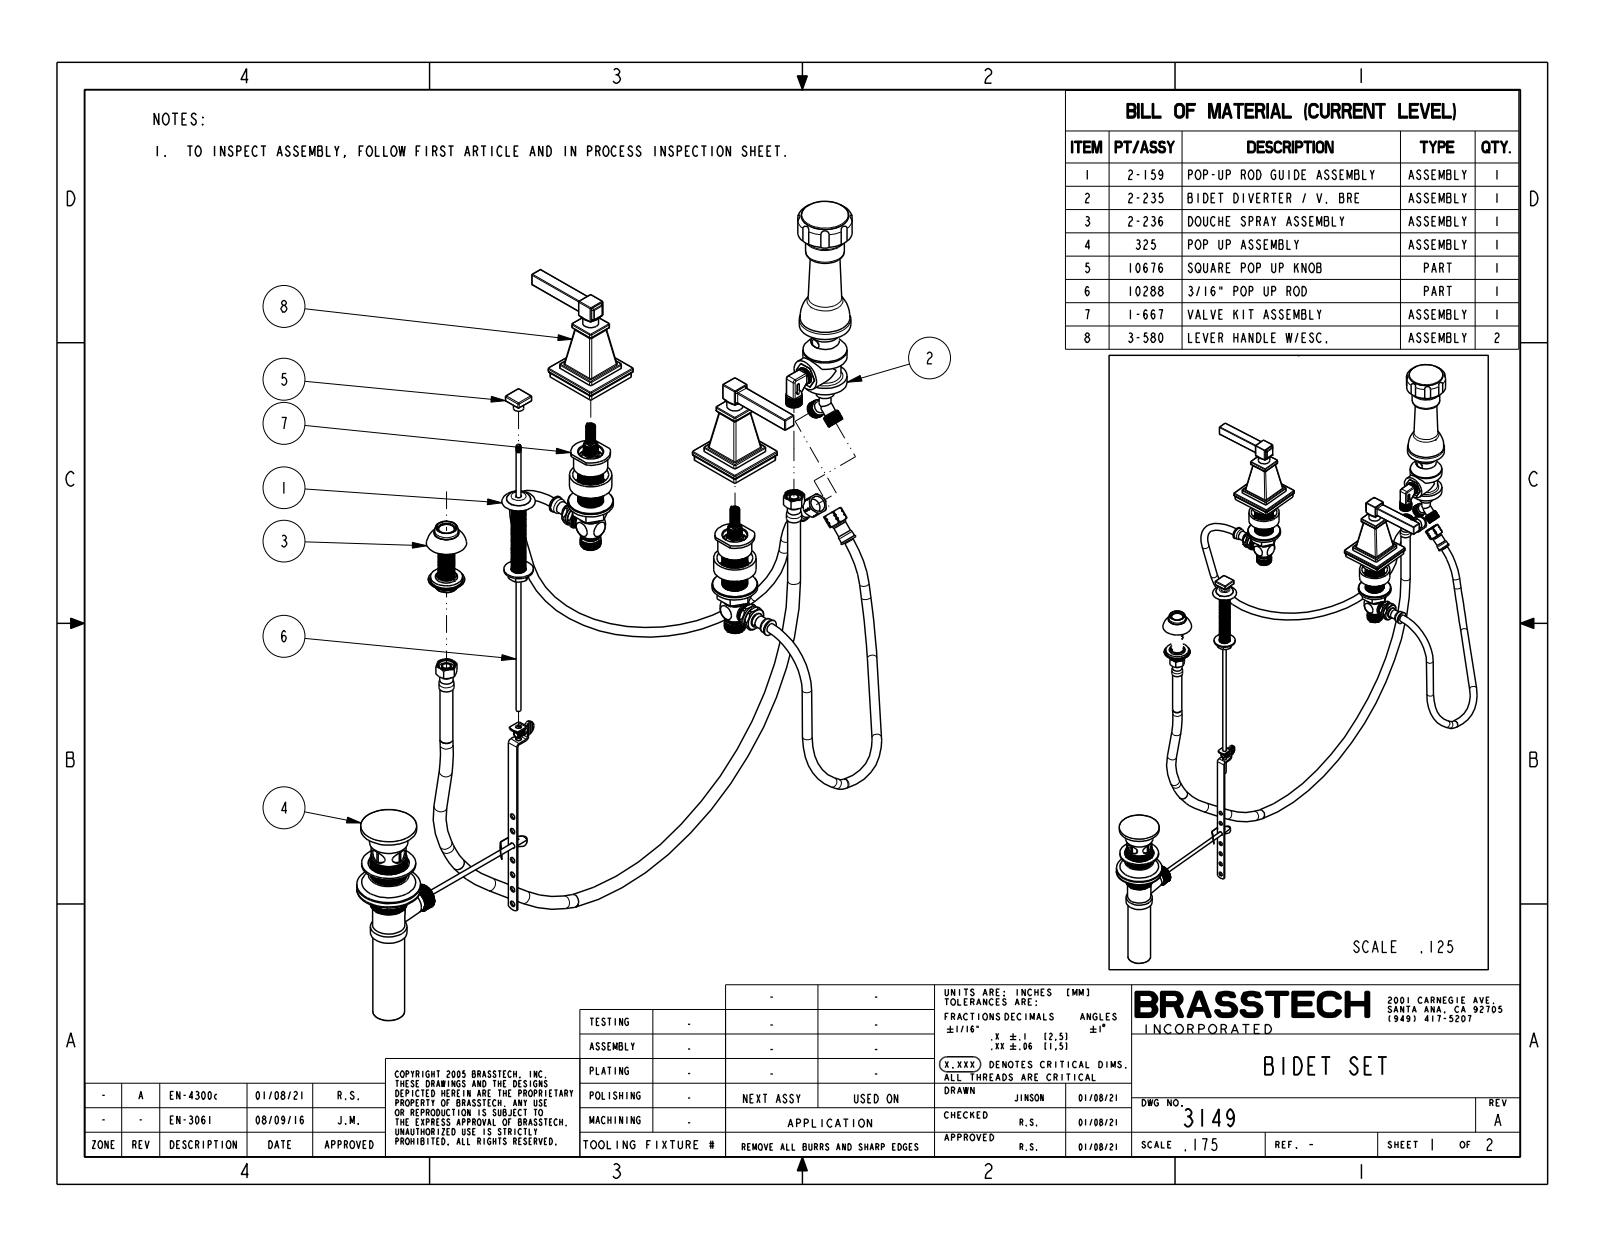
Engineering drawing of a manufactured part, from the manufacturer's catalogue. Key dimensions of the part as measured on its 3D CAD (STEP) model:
Part name (STEP PRODUCT): 3149
STEP written by: CREO PARAMETRIC BY PTC INC, 2018400 (CONFIG_CONTROL_DESIGN)
Units: inches
Bodies: 5 solids, 623 faces (133 planar, 244 cylindrical, 246 other)
Overall size (bounding box): 22.855 × 14.063 × 5.353
Volume: 25.54 in³ · Surface area: 116.5 in²
Round holes (diameter × count): ⌀0.625 ×1, ⌀0.792 ×1, ⌀0.94 ×1
Round bosses / shafts (diameter × count): ⌀0.625 ×2, ⌀0.506 ×2, ⌀2.025 ×1, ⌀1.52 ×1, ⌀0.925 ×1, ⌀0.775 ×1, ⌀0.4 ×1
Partial cylindrical surfaces — rounded edges, fillets, slot ends (radius × count): R0.03 ×76, R0.06 ×56, R0.04 ×12, R0.09 ×12, R0.21 ×8, R0.23 ×8, R0.357 ×1, R1.077 ×1
Main face-to-face distances: 0.41, 0.5, 7.88, 0.593, 0.093, 3.035, 3.535, 2.625, 3.125, 0.272
